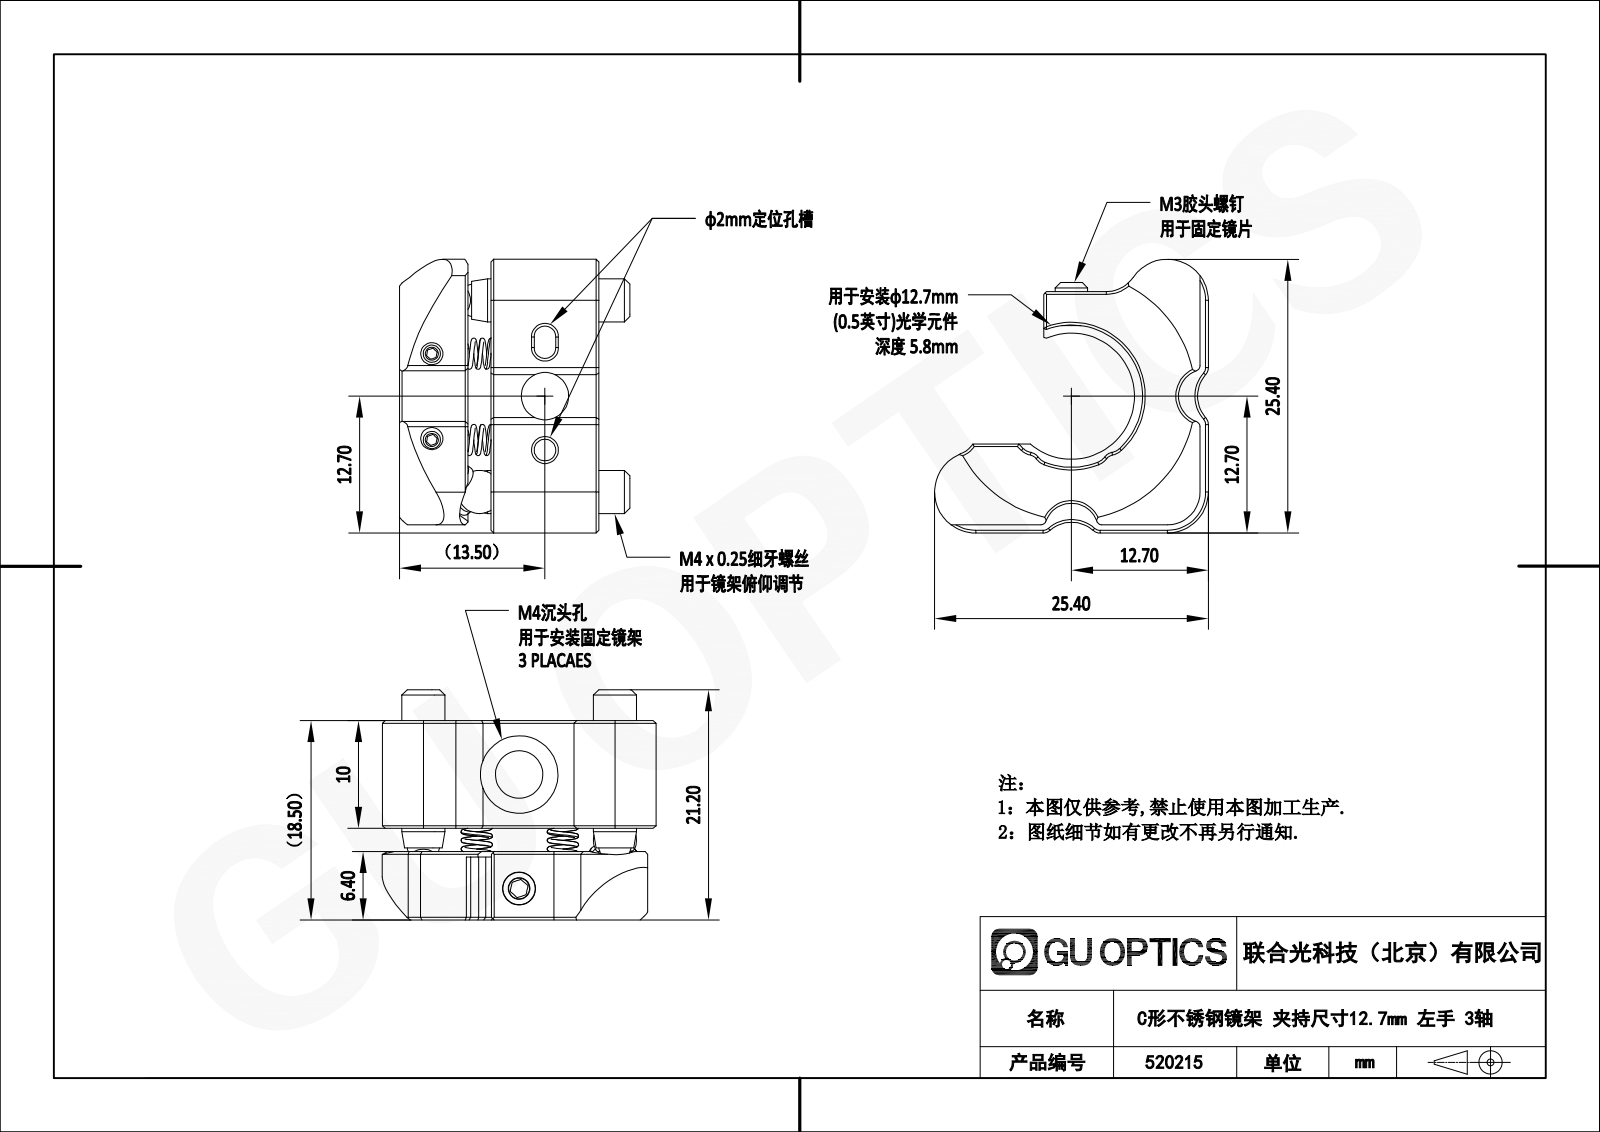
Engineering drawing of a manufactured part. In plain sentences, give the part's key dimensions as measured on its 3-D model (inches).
The part is named "520215". Its 3-D file was written by "SolidWorks 2020 (CONFIG_CONTROL_DESIGN)". It is 25 solids with 413 faces: 183 planar, 91 cylindrical and 139 other. Overall it measures 1 by 1 by 0.835 inches. Its volume is 0.235 cubic inches and its surface area 8.647 square inches. Round holes: 4 of diameter 0.063, 4 of diameter 0.126, 4 of diameter 0.134, 3 of diameter 0.118, 3 of diameter 0.148, 3 of diameter 0.171, 2 of diameter 0.079, 2 of diameter 0.173, 2 of diameter 0.283, 1 of diameter 0.098. Round bosses or shafts: 6 of diameter 0.102, 5 of diameter 0.079, 3 of diameter 0.157, 2 of diameter 0.059, 1 of diameter 0.118. Partial cylindrical surfaces (rounded edges, fillets, slot ends): 8 of radius 0.039, 5 of radius 0.15, 4 of radius 0.02, 4 of radius 0.059, 3 of radius 0.098, 3 of radius 0.118, 2 of radius 0.045, 2 of radius 0.197. The main face-to-face distances are 0.079, 0.394, 0.329, 0.722, 0.25, 0.472, 0.221, 0.02, 0.3, 0.23. The hole center spacings are 0.31, 0.195, 0.436, 0.505, 0.197, 0.542, 0.7, 0.727.
